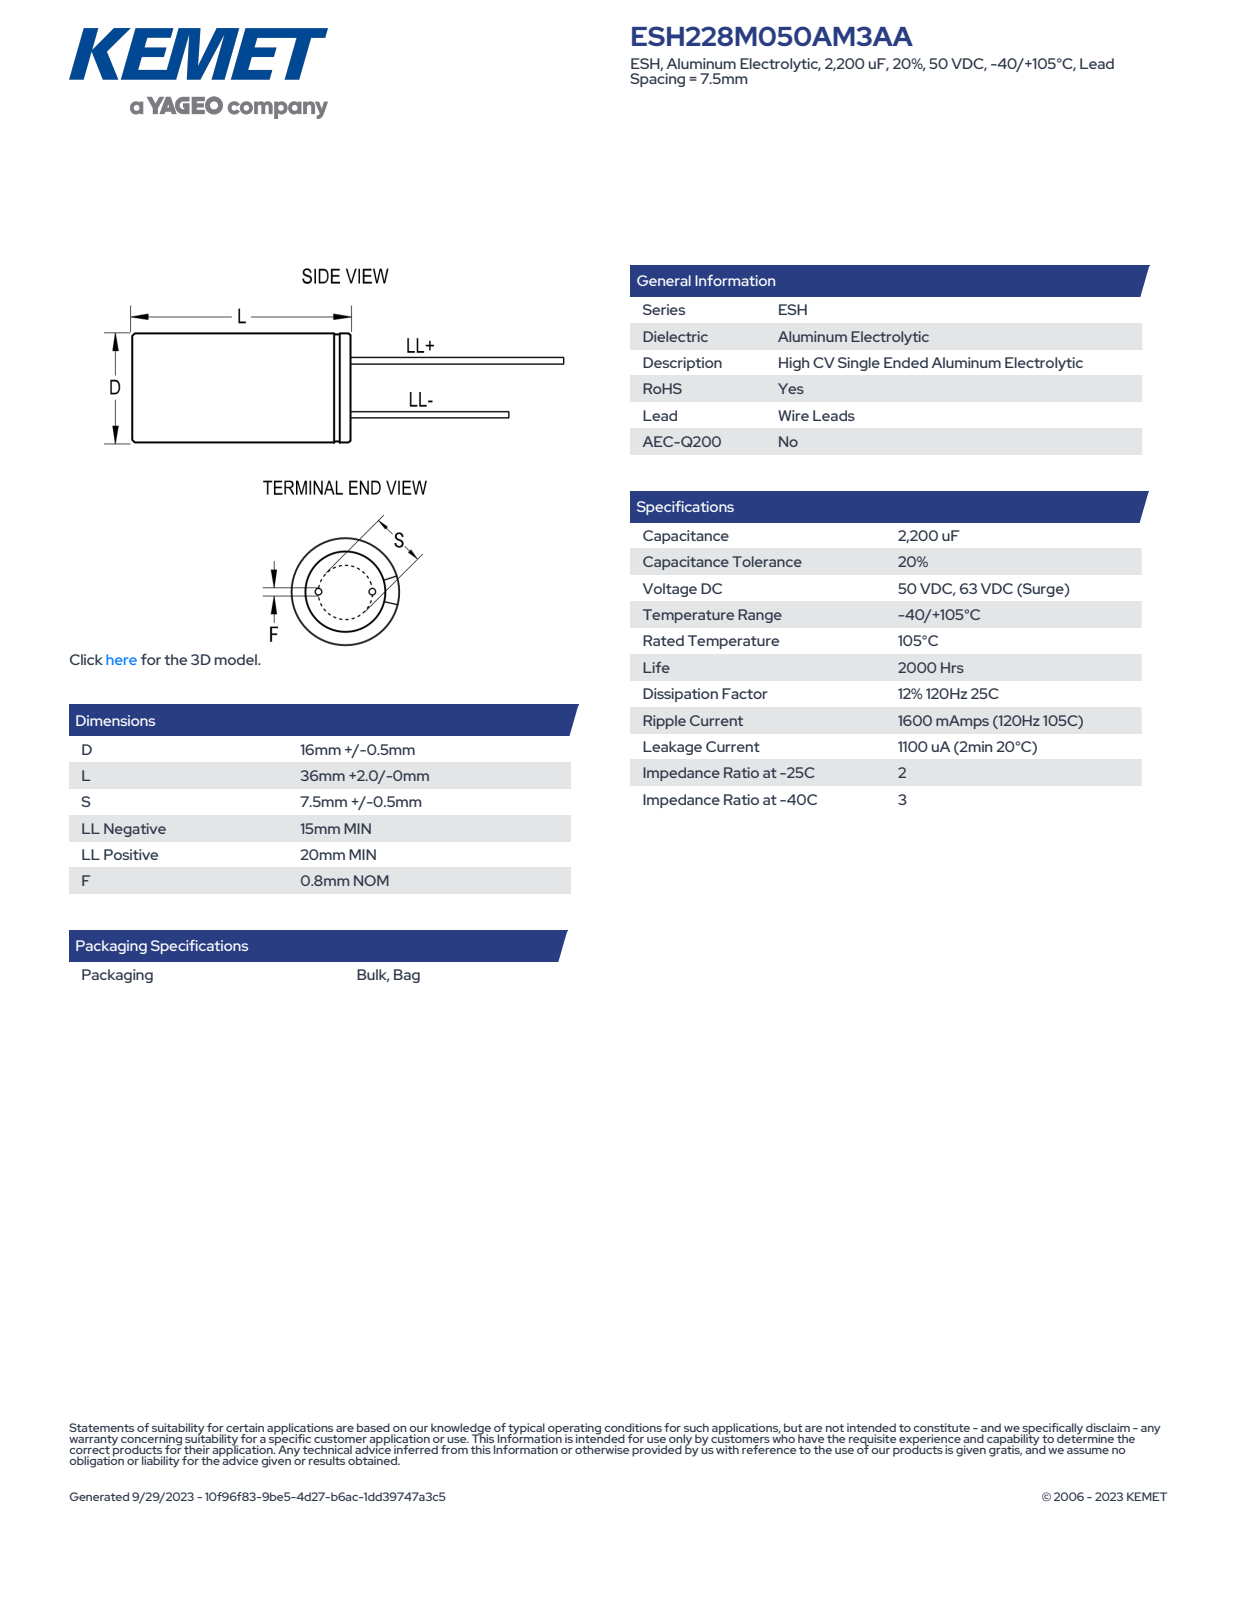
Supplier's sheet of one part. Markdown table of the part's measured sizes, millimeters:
| quantity | value |
| --- | --- |
| part name | CAR_KLP_16X36_D16.5L38S7.5F0.8 |
| STEP written by | SolidWorks 2014 (AUTOMOTIVE_DESIGN) |
| units | millimeters |
| bodies | 4 solids, 75 faces (61 planar, 8 cylindrical, 6 other) |
| overall size | 58.01 × 16.5 × 16.5 |
| volume | 8 096 mm³ |
| surface area | 2 549 mm² |
| round bosses / shafts (diameter × count) | 0.8 × 2, 16.5 × 1 |
| main face-to-face distances | 38, 38.01, 5, 53.01, 58.01, 53, 58, 15, 20, 2.22 |
